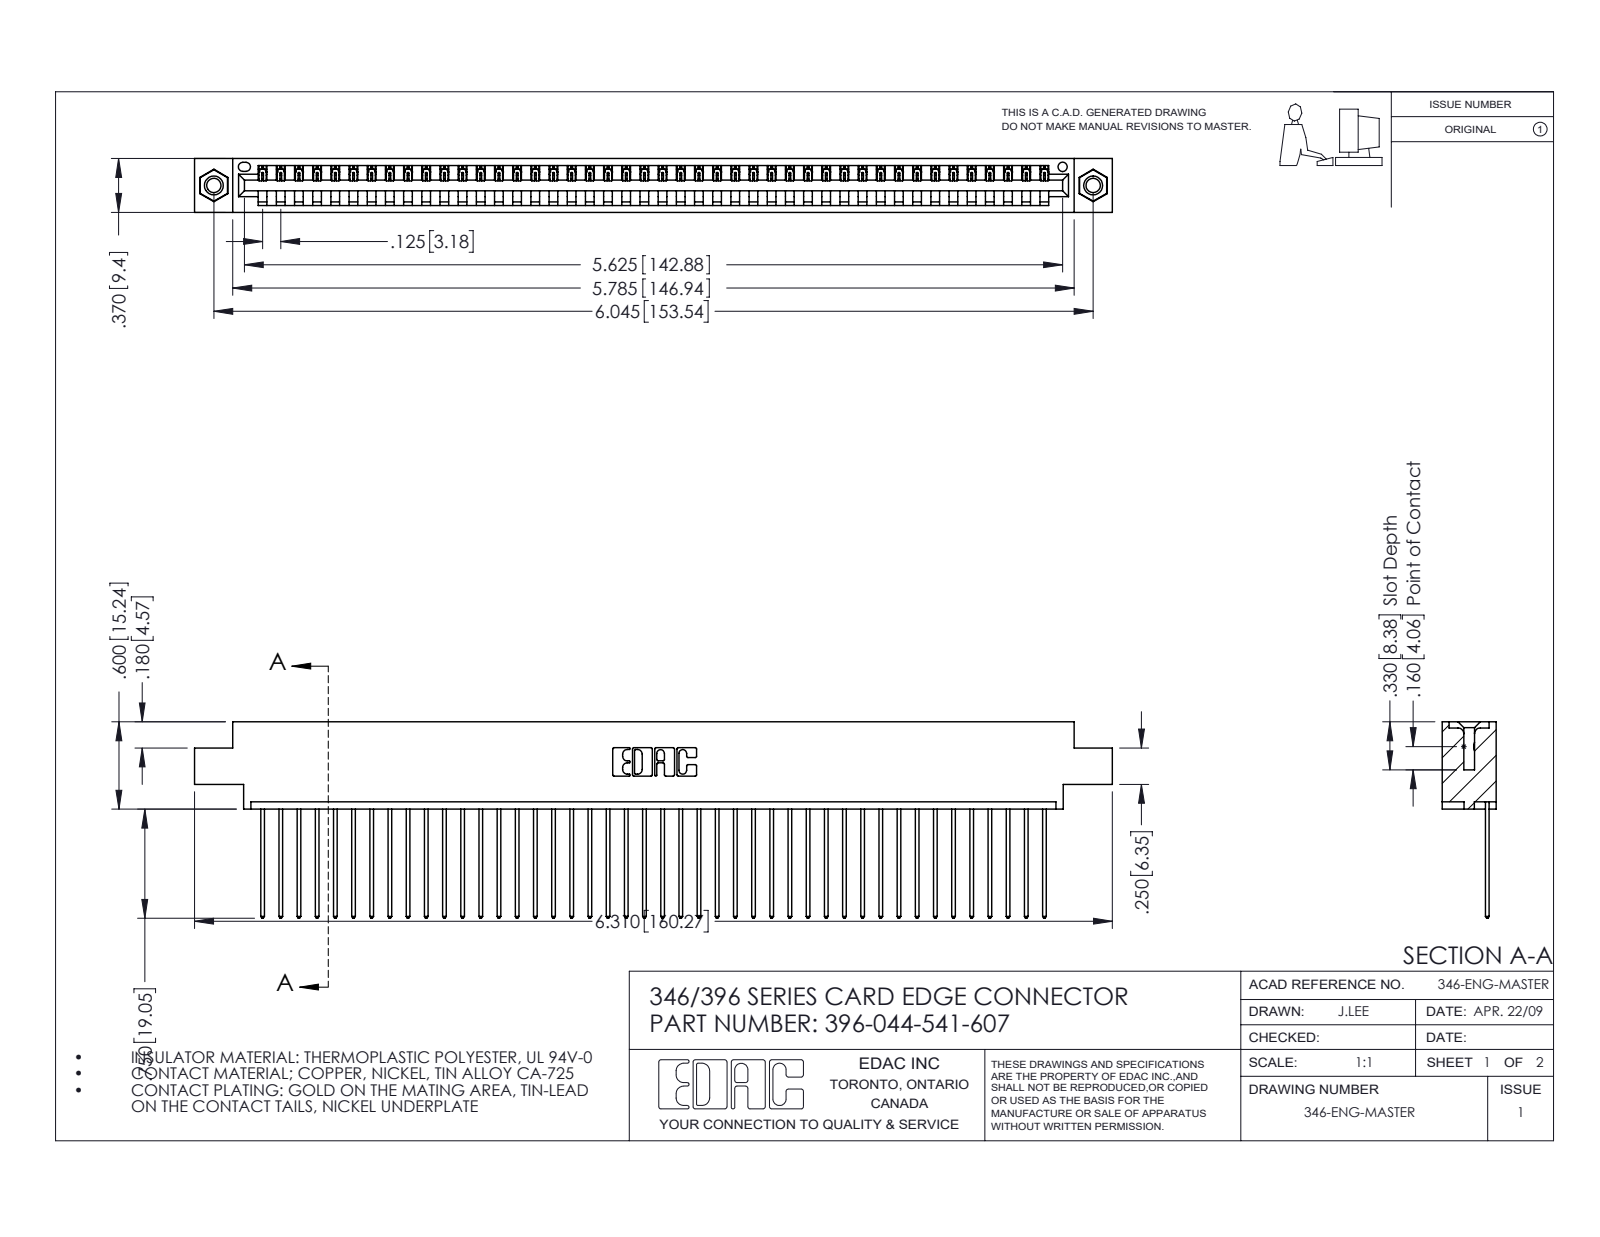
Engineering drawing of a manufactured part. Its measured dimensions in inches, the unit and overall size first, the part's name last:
Units: inches
Overall size (bounding box): 6.31 × 1.35 × 0.37
Round holes (diameter × count): ⌀0.098 ×2, ⌀0.125 ×2, ⌀0.156 ×2, ⌀0.064 ×1
Round bosses / shafts (diameter × count): ⌀0.155 ×2
Partial cylindrical surfaces — rounded edges, fillets, slot ends (radius × count): R0.006 ×88, R0.01 ×88, R0.01 ×22, R0.007 ×6, R0.031 ×6, R0.026 ×3, R0.031 ×2, R0.04 ×2
Main face-to-face distances: 0.048, 0.322, 0.37, 0.25, 0.072, 0.298, 0.025, 0.222, 0.148, 0.1
Hole centre spacings: 0.246, 5.836, 6.045
Volume: 0.936 in³ · Surface area: 31.38 in²
Bodies: 47 solids, 2738 faces (1872 planar, 850 cylindrical, 16 other)
Part name (STEP PRODUCT): 346 Part_0.170 Offset - 0.156 Dia-TI; 345-292-001_345-293-141; 396-044-541-607; 345-250-001_345-250-005-103
STEP written by: SolidWorks 2016 (CONFIG_CONTROL_DESIGN)
